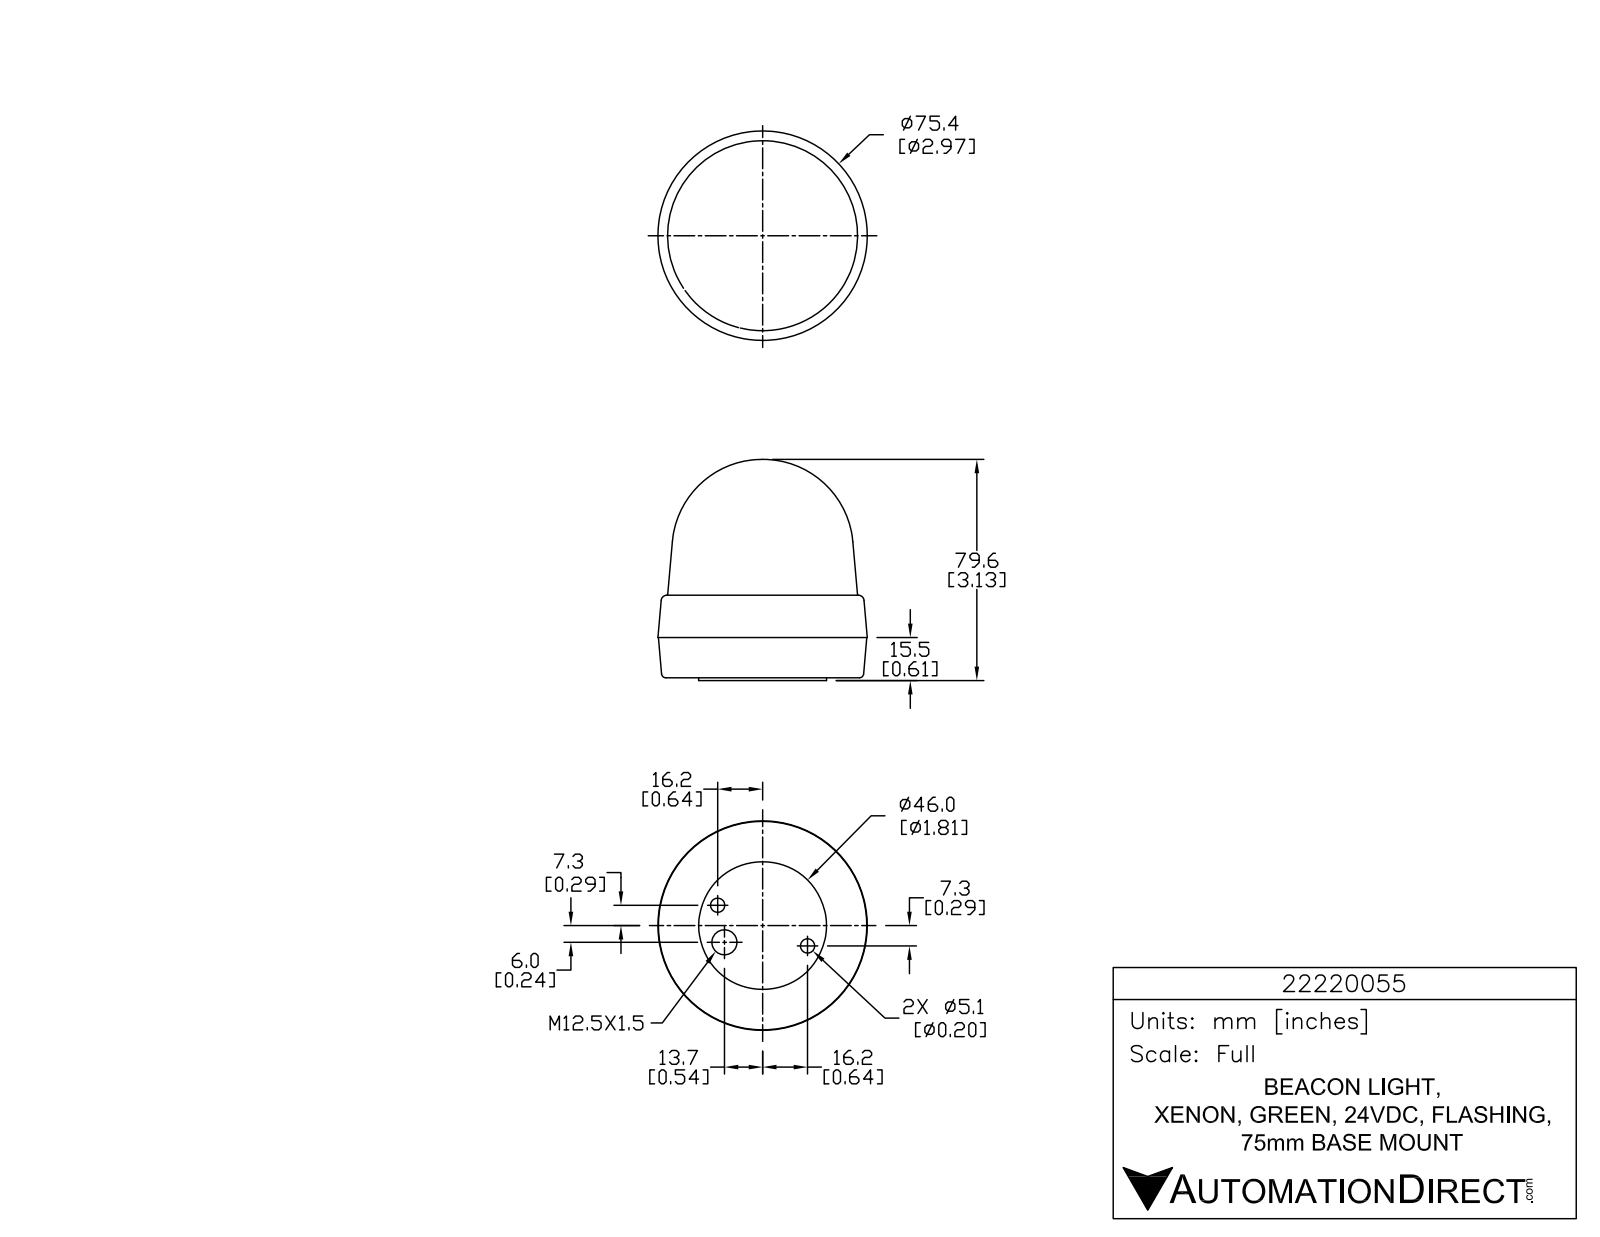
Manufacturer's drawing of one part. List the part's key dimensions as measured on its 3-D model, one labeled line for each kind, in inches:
Part name (STEP PRODUCT): 22220055
STEP written by: SolidWorks 2015 (AUTOMOTIVE_DESIGN)
Units: inches
Bodies: 1 solid, 773 faces (526 planar, 163 cylindrical, 84 other)
Overall size (bounding box): 3.133 × 2.967 × 2.967
Volume: 15.79 in³ · Surface area: 33.7 in²
Round holes (diameter × count): ⌀0.059 ×3, ⌀0.201 ×2, ⌀0.354 ×1
Round bosses / shafts (diameter × count): ⌀0.339 ×3, ⌀0.084 ×3, ⌀1.811 ×1
Partial cylindrical surfaces — rounded edges, fillets, slot ends (radius × count): R0.005 ×9, R0.005 ×6, R0.012 ×6, R0.012 ×6, R0.012 ×6, R0.196 ×6, R0.005 ×3, R0.005 ×3
Main face-to-face distances: 0.039, 1.209, 1.17, 0.61, 0.571, 0.599, 1.566, 1.527, 0.956, 0.357
Hole centre spacings: 0.534, 1.179, 1.398
